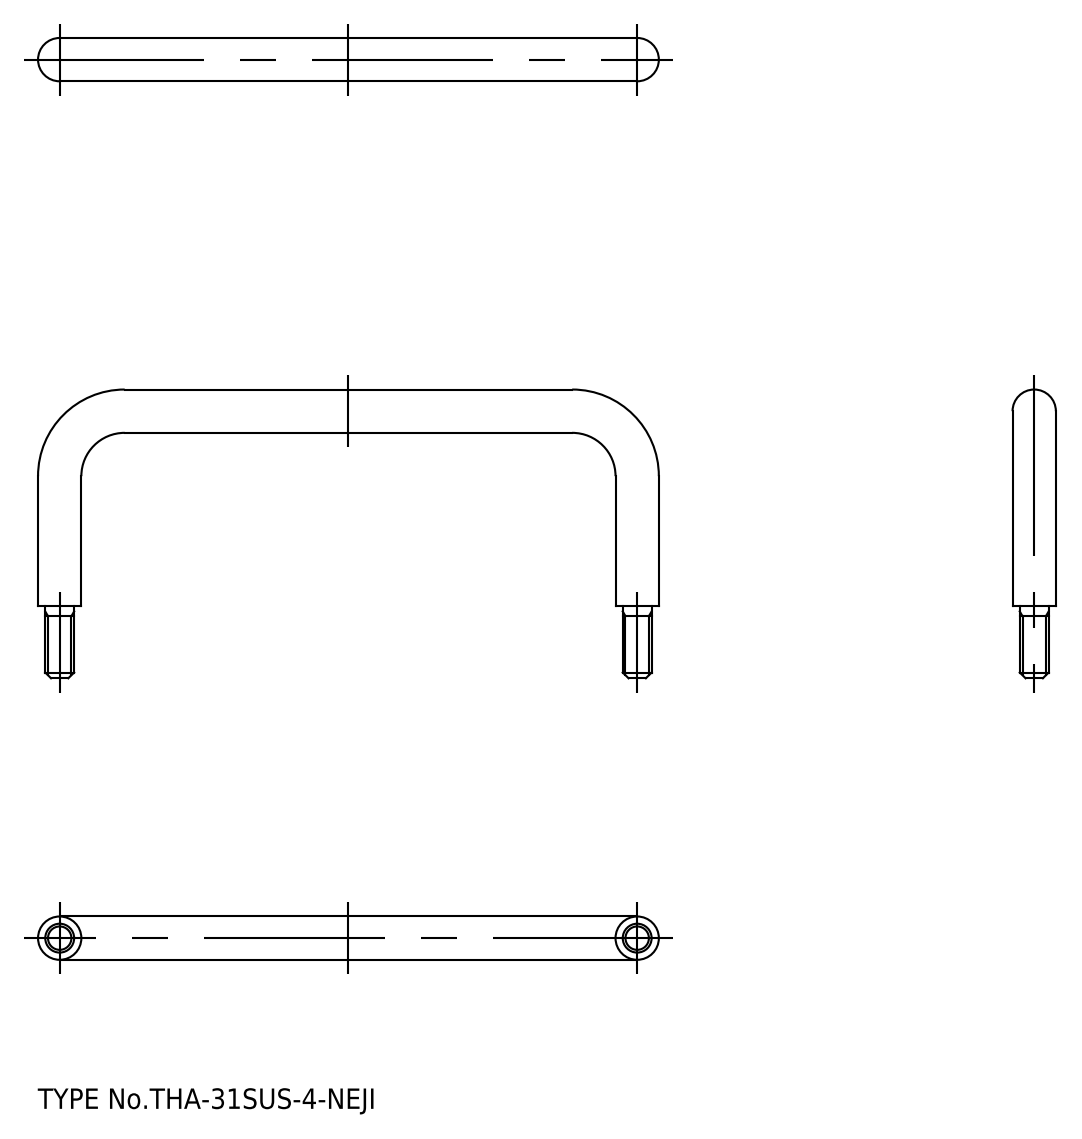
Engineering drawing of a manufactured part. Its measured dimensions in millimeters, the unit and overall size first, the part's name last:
Units: millimetres
Overall size (bounding box): 86 × 40 × 6
Round bosses / shafts (diameter × count): ⌀6 ×3, ⌀4 ×2
Main face-to-face distances: 10
Volume: 3 819 mm³ · Surface area: 2 680 mm²
Bodies: 1 solid, 22 faces (4 planar, 10 cylindrical, 8 other)
STEP written by: spGate 17.5.2 (AUTOMOTIVE_DESIGN)
